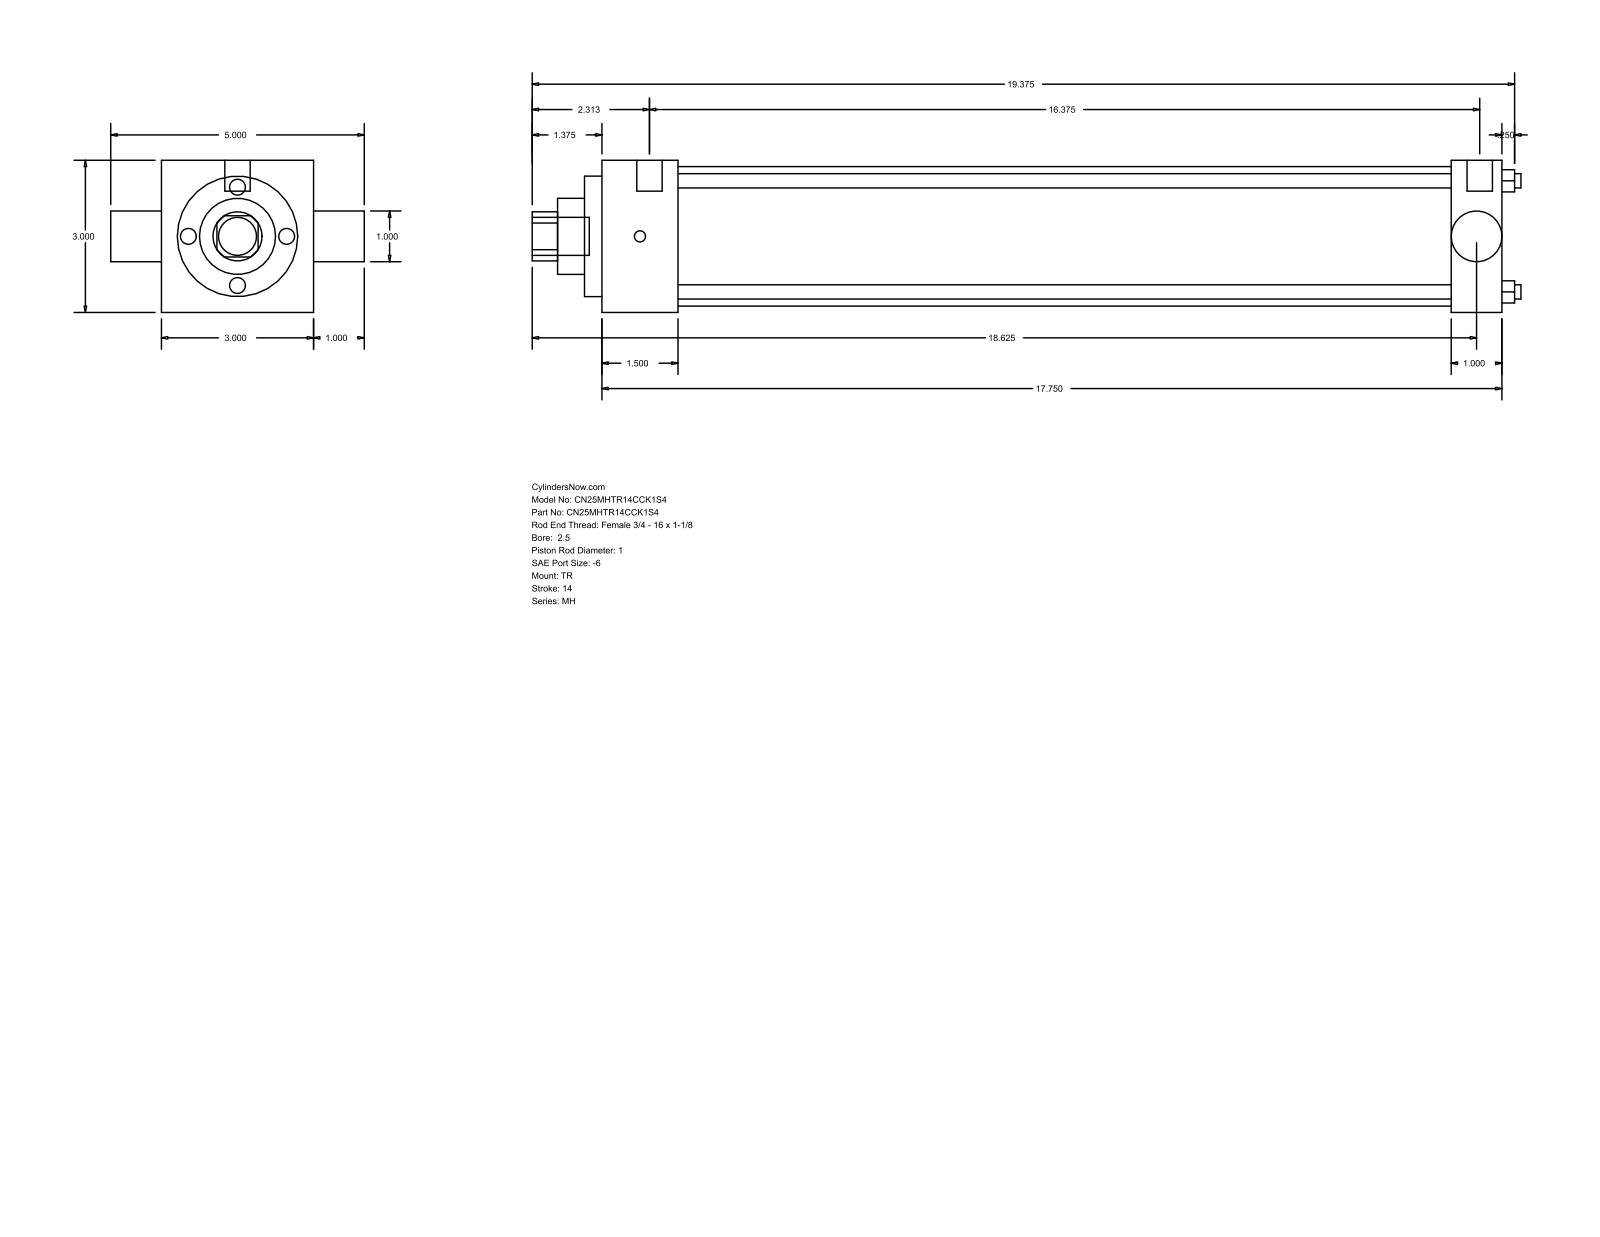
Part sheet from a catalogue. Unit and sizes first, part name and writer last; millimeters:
Units: millimetres
Overall size (bounding box): 495.3 × 127 × 76.2
Round holes (diameter × count): ⌀7.14 ×4, ⌀25.35 ×1, ⌀25.4 ×1, ⌀38.1 ×1, ⌀60.33 ×1, ⌀69.85 ×1
Round bosses / shafts (diameter × count): ⌀5.56 ×3, ⌀12.7 ×2, ⌀19.05 ×1
Partial cylindrical surfaces — rounded edges, fillets, slot ends (radius × count): R12.29 ×1
Main face-to-face distances: 76.2, 450.85, 25.39, 38.11, 412.74, 425.46, 387.35, 8.73, 46.84, 434.19
Hole centre spacings: 39.33, 55.62, 78.66
Bodies: 0 solids, 86 faces (61 planar, 25 cylindrical, 0 other)
Part name (STEP PRODUCT): MH_TR__0250_1
STEP written by: GSSL Pune (CONFIG_CONTROL_DESIGN)
